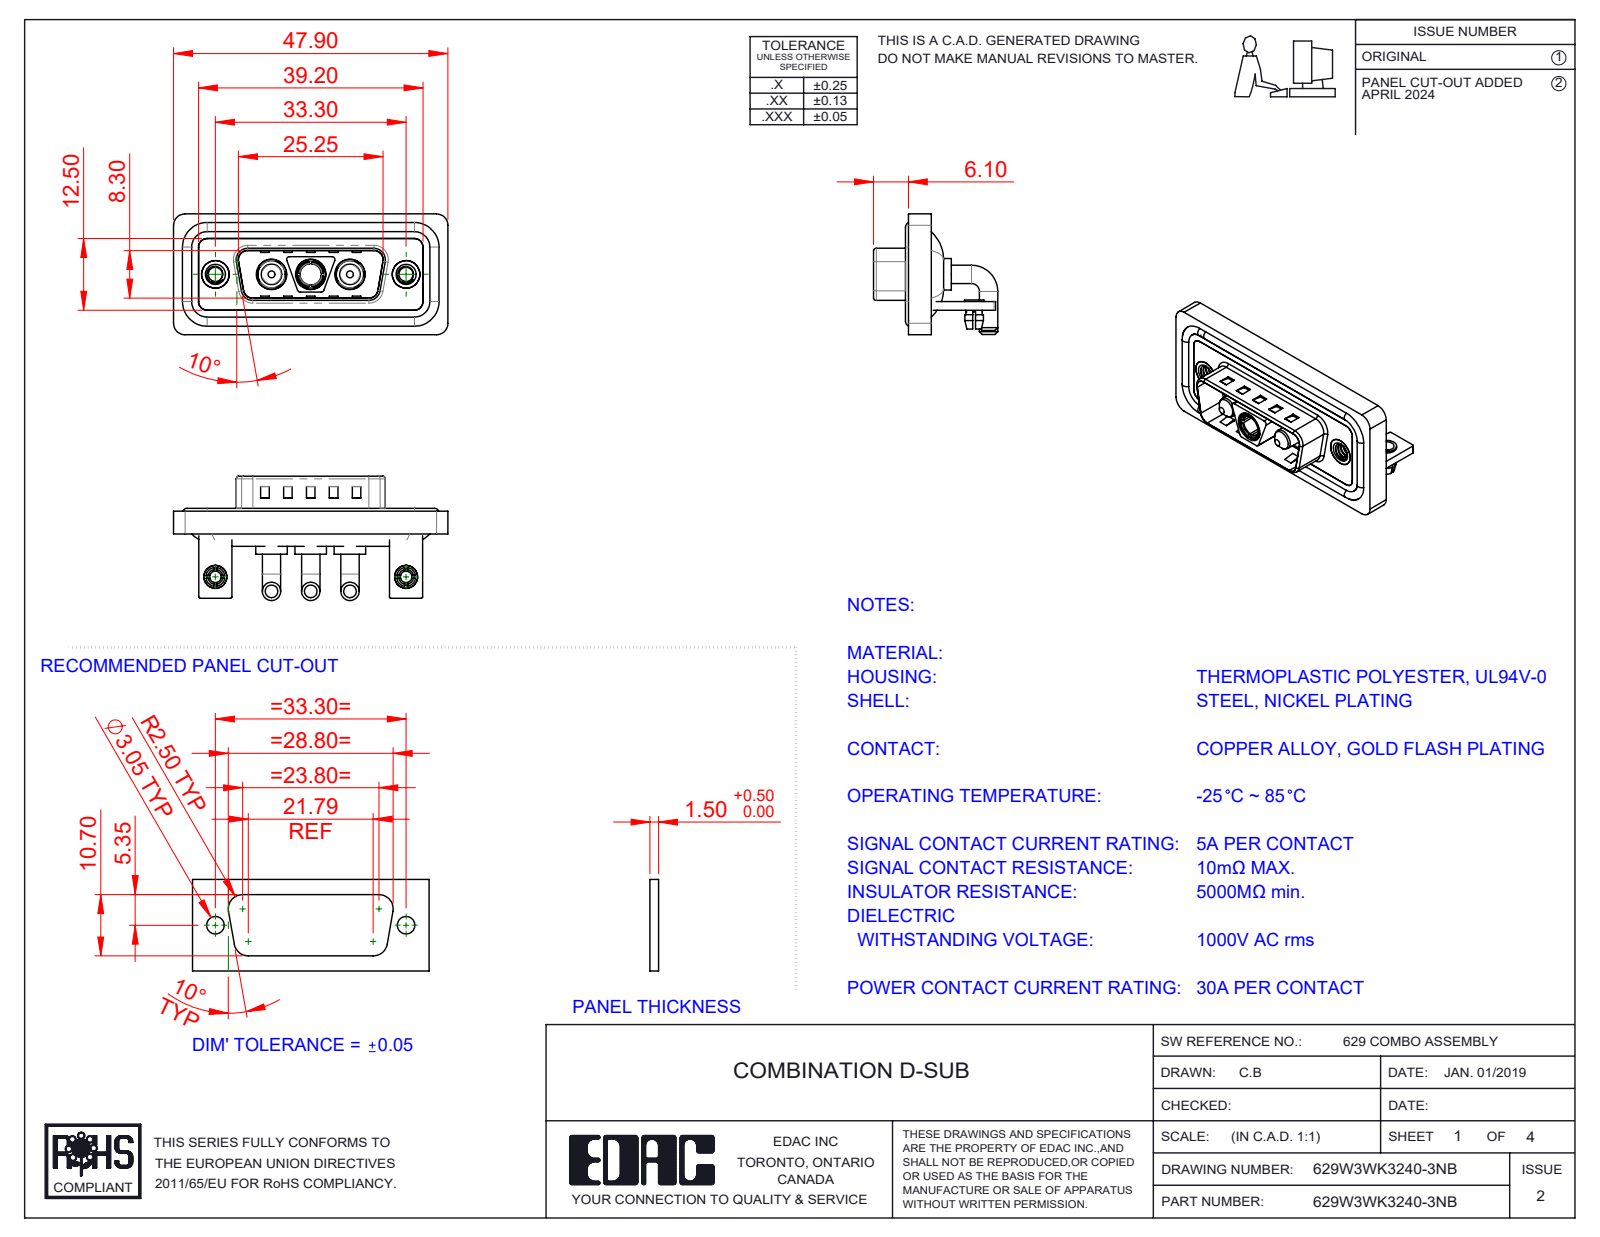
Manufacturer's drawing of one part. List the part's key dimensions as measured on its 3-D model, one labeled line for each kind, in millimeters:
Part name (STEP PRODUCT): 629Combo Threaded Rivet_B; 629Combo Shell Rear_15 Contacts; 629Combo Waterproof Housing_15 Contacts; 629W3WK3140-3NB (+6 more)
STEP written by: SolidWorks 2023 (CONFIG_CONTROL_DESIGN)
Units: millimetres
Bodies: 17 solids, 751 faces (299 planar, 306 cylindrical, 146 other)
Overall size (bounding box): 47.9 × 21.7 × 21.1
Volume: 6 279 mm³ · Surface area: 10 271 mm²
Round holes (diameter × count): ⌀2.5 ×4, ⌀4.85 ×3, ⌀5.3 ×3, ⌀2 ×2, ⌀3.2 ×2, ⌀4 ×2, ⌀4.8 ×2, ⌀5 ×2, ⌀3.7 ×1
Round bosses / shafts (diameter × count): ⌀3.2 ×6, ⌀1.6 ×4, ⌀5.5 ×3, ⌀5.2 ×3, ⌀4.75 ×3, ⌀3.75 ×3, ⌀4.9 ×2, ⌀4 ×2
Partial cylindrical surfaces — rounded edges, fillets, slot ends (radius × count): R2 ×21, R1.5 ×18, R0.25 ×16, R0.5 ×13, R1.6 ×8, R0.6 ×4, R0.65 ×4, R0.9 ×4
Main face-to-face distances: 0.4, 1.5, 0.8, 2.9, 1.1, 2.1, 3.7, 1.6, 1.2, 4.5
Hole centre spacings: 6.85, 9.8, 16.65, 23.5, 33.3, 13.7
